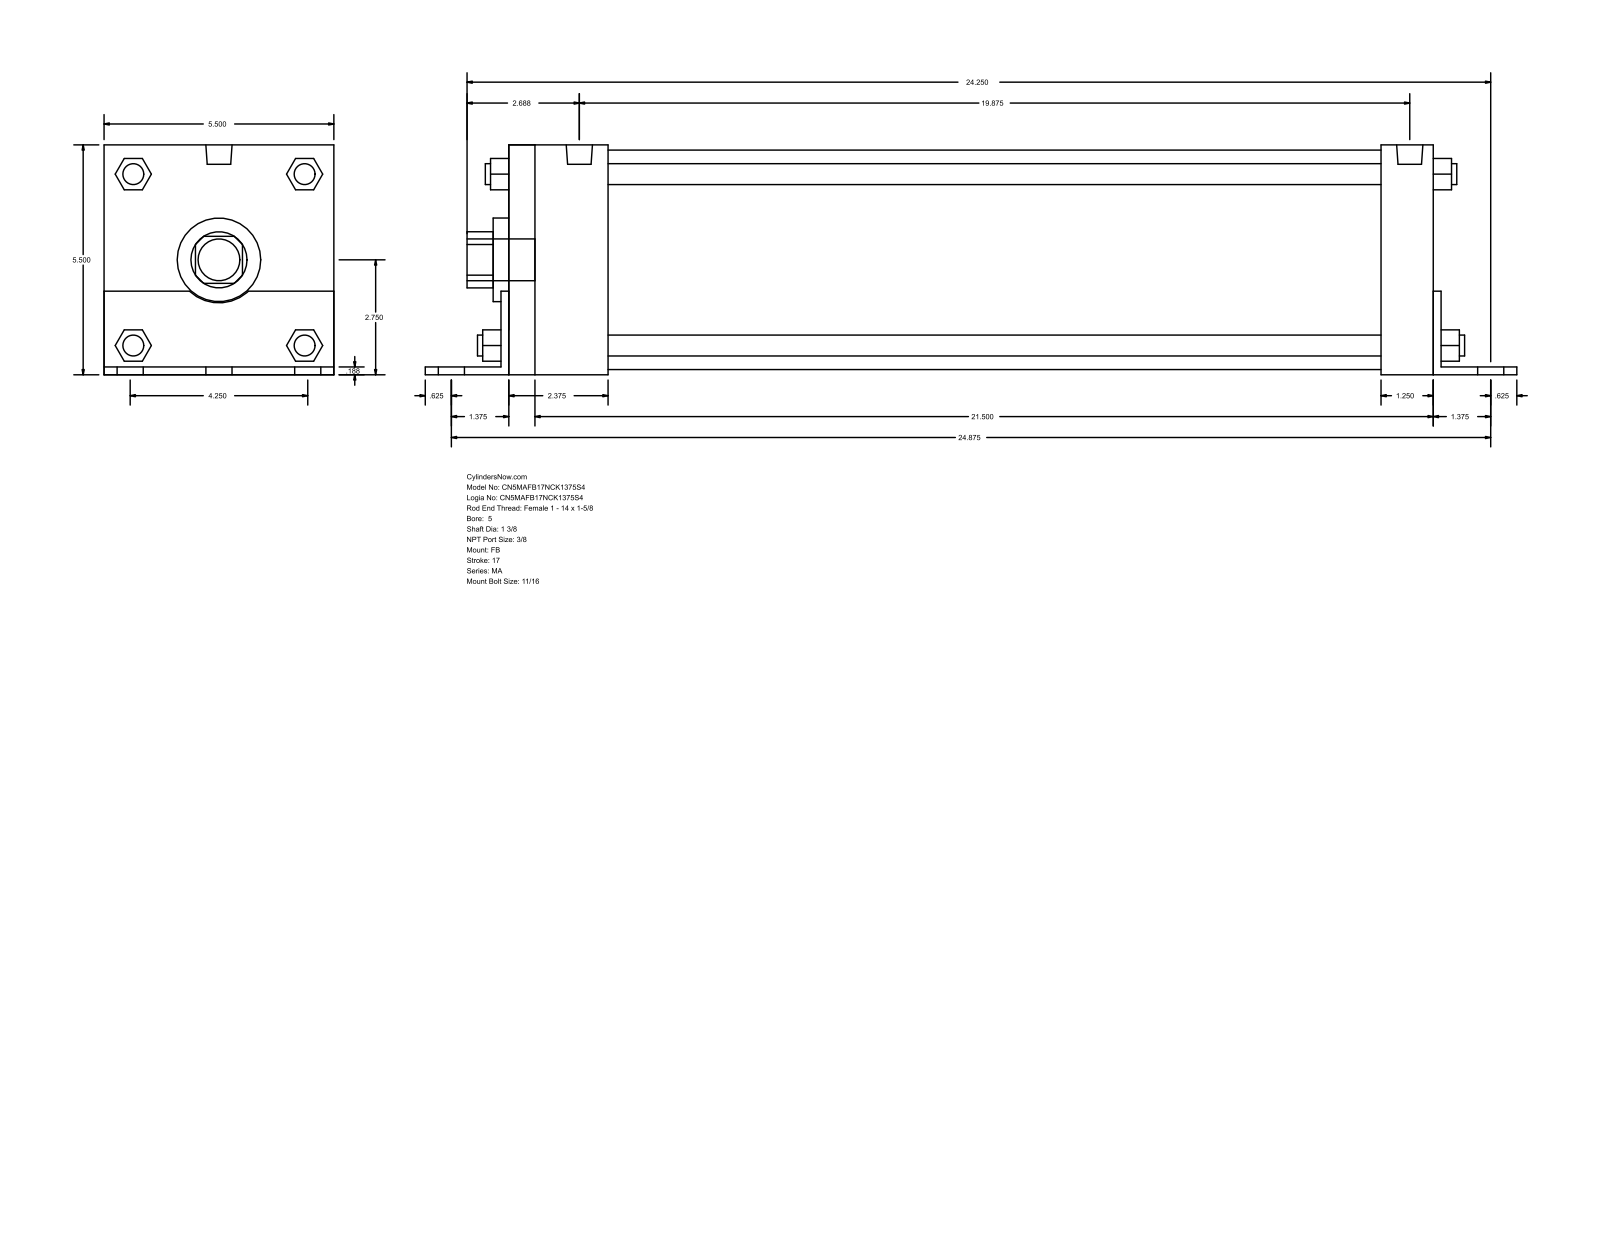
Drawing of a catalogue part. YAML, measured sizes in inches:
part_name: "MA_FB__0500_1.375"
step_written_by: "GSSL Pune (CONFIG_CONTROL_DESIGN)"
units: inches
bodies: {solids: 0, faces: 140, planar: 105, cylindrical: 35, other: 0}
overall_size: [26.125, 5.502, 5.5]
round_holes:
  - {diameter: 1.375, count: 1}
  - {diameter: 2, count: 1}
  - {diameter: 5.25, count: 1}
round_bosses_or_shafts:
  - {diameter: 0.687, count: 6}
  - {diameter: 0.5, count: 4}
  - {diameter: 0.437, count: 4}
  - {diameter: 0.627, count: 2}
  - {diameter: 1, count: 1}
partial_cylinders:
  - {radius: 0.672, count: 1}
  - {radius: 1.03, count: 1}
face_to_face_distances: [5.5, 0.187, 5.502, 22.313, 0.185, 5.315, 22.125, 22.5, 2.562, 2.375]
